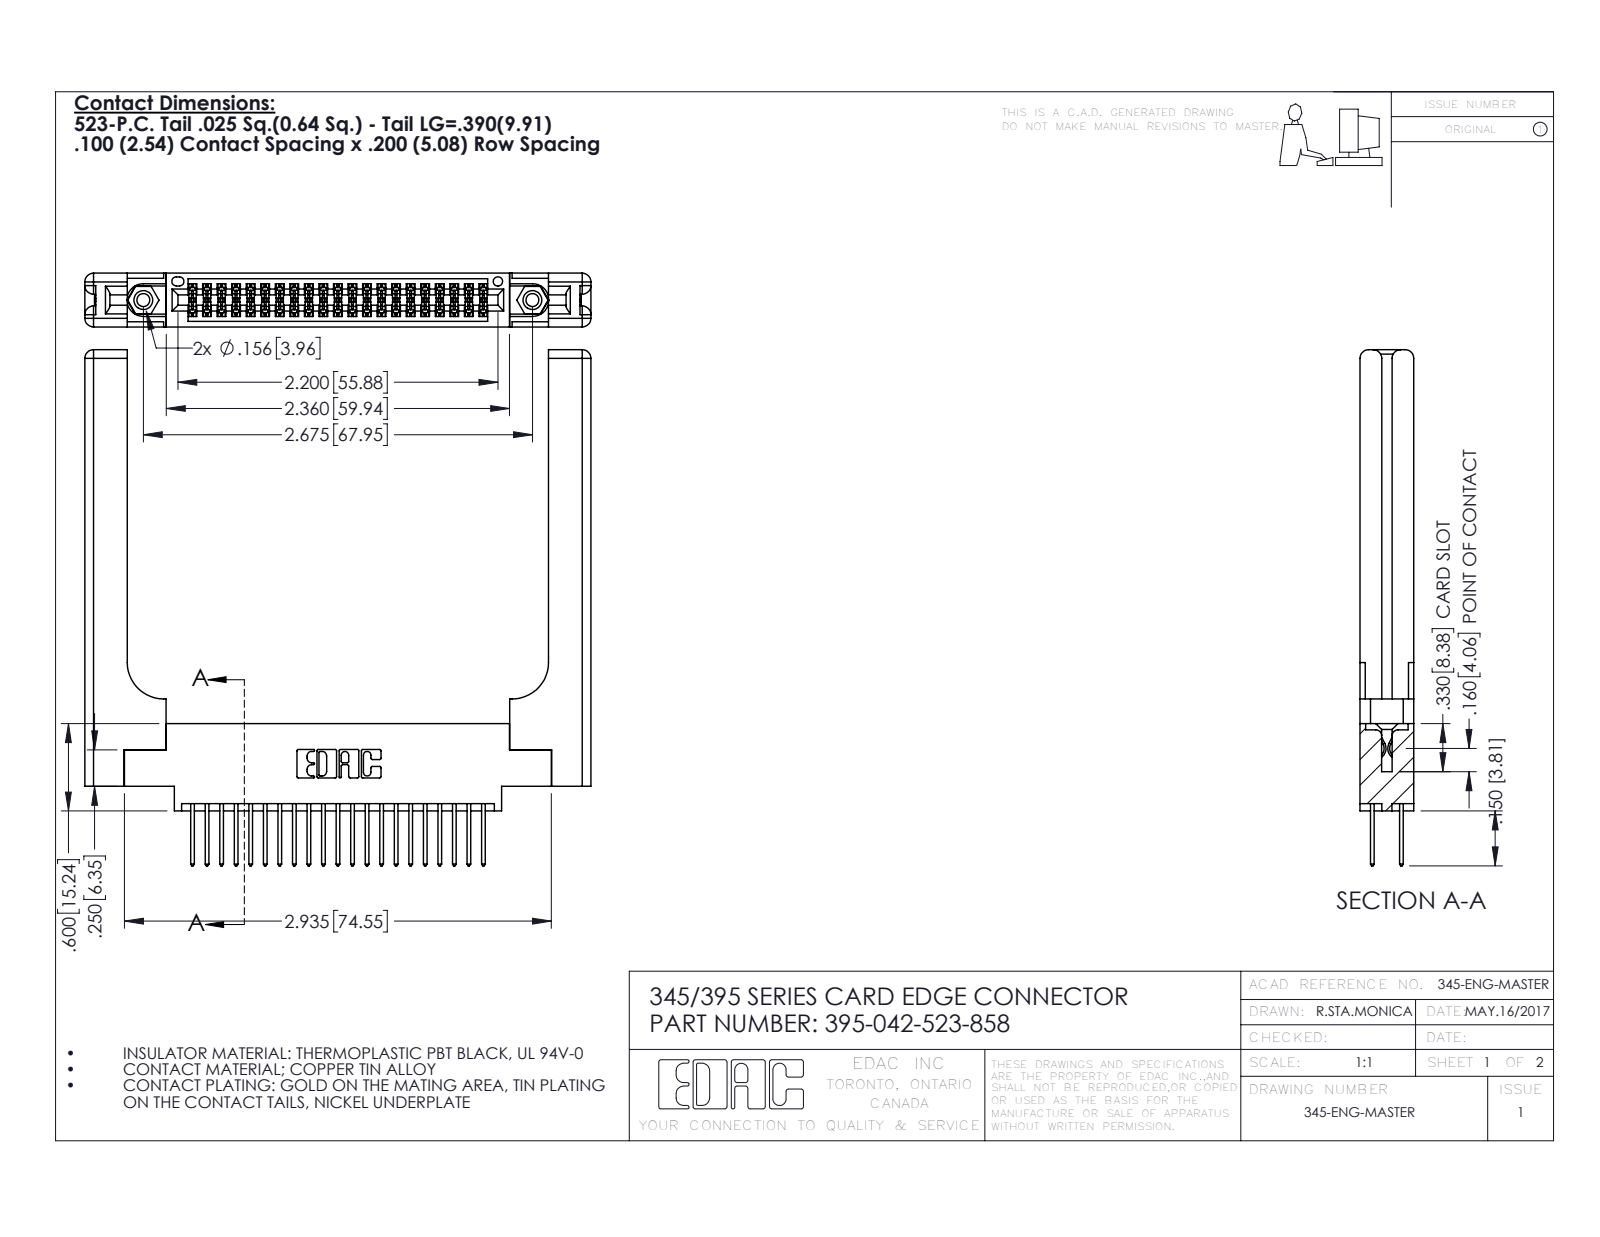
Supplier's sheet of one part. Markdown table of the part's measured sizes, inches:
| quantity | value |
| --- | --- |
| part name | 345-250-001_345-250-001-102; 345-292-001_345-293-123; 395-042-523-858; 345 Part_0.170 Offset - 0.156 Dia-TH (+1 more) |
| STEP written by | SolidWorks 2016 (CONFIG_CONTROL_DESIGN) |
| units | inches |
| bodies | 47 solids, 2486 faces (1618 planar, 808 cylindrical, 60 other) |
| overall size | 3.547 × 3.479 × 0.37 |
| volume | 1.027 in³ |
| surface area | 27.19 in² |
| round holes (diameter × count) | 0.089 × 2, 0.125 × 2, 0.156 × 2, 0.064 × 1 |
| round bosses / shafts (diameter × count) | 0.155 × 2 |
| partial cylindrical surfaces (radius × count) | 0.006 × 63, 0.01 × 42, 0.01 × 22, 0.06 × 16, 0.007 × 6, 0.031 × 6, 0.026 × 3, 0.014 × 2 |
| main face-to-face distances | 0.37, 0.072, 0.298, 0.098, 0.272, 0.025, 0.2, 0.225, 0.148, 0.15 |
| hole center spacings | 0.27, 2.441, 2.675 |
